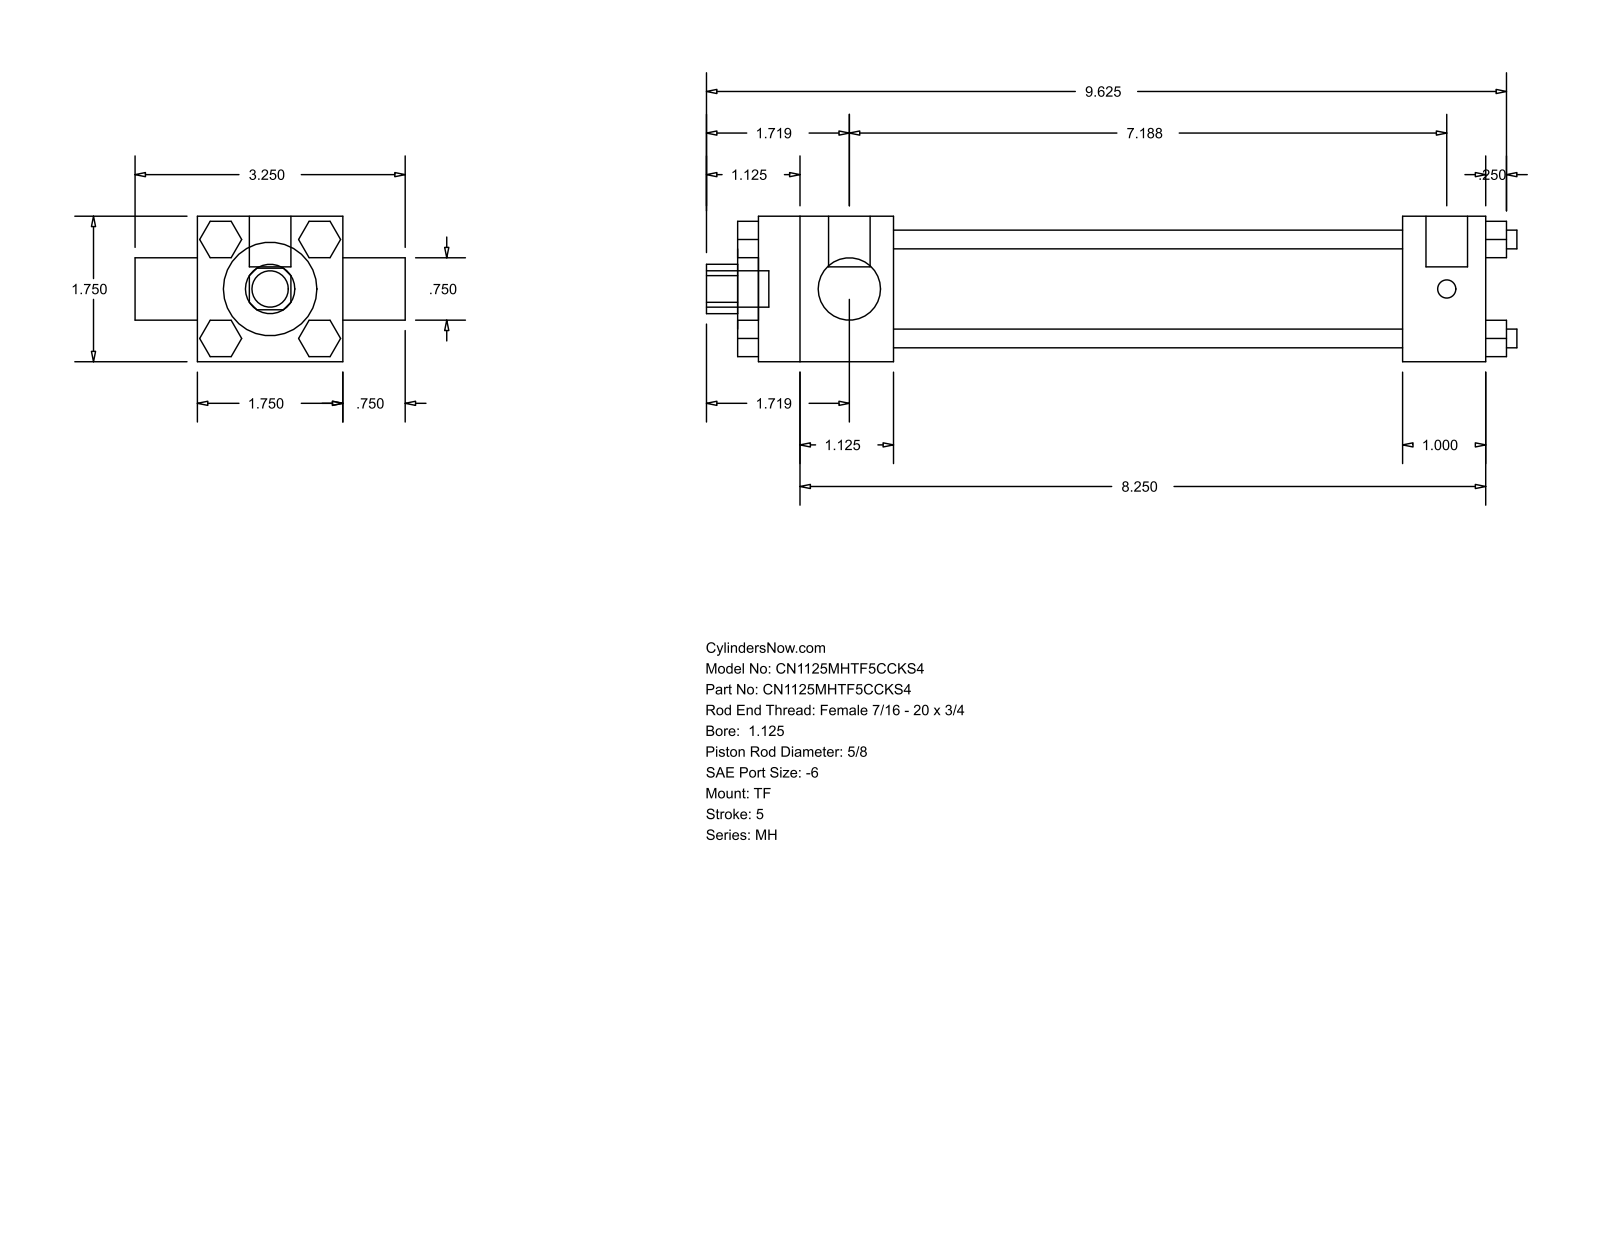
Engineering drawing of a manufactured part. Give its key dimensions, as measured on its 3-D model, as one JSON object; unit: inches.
{"part_name": "MH_TF__0112_0.625", "step_written_by": "GSSL Pune (CONFIG_CONTROL_DESIGN)", "units": "inches", "bodies": {"solids": 0, "faces": 120, "planar": 92, "cylindrical": 28, "other": 0}, "overall_size": [9.75, 3.25, 1.75], "round_holes": [[0.625, 1], [0.75, 1], [1.125, 1], [1.375, 1]], "round_bosses_or_shafts": [[0.225, 4], [0.219, 3], [0.5, 2], [0.437, 1]], "partial_cylinders_radius": [[0.297, 1]], "face_to_face_distances": [1.75, 0.25, 9, 0.437, 6.125, 7.125, 1, 1.625, 7.75, 8.75]}
